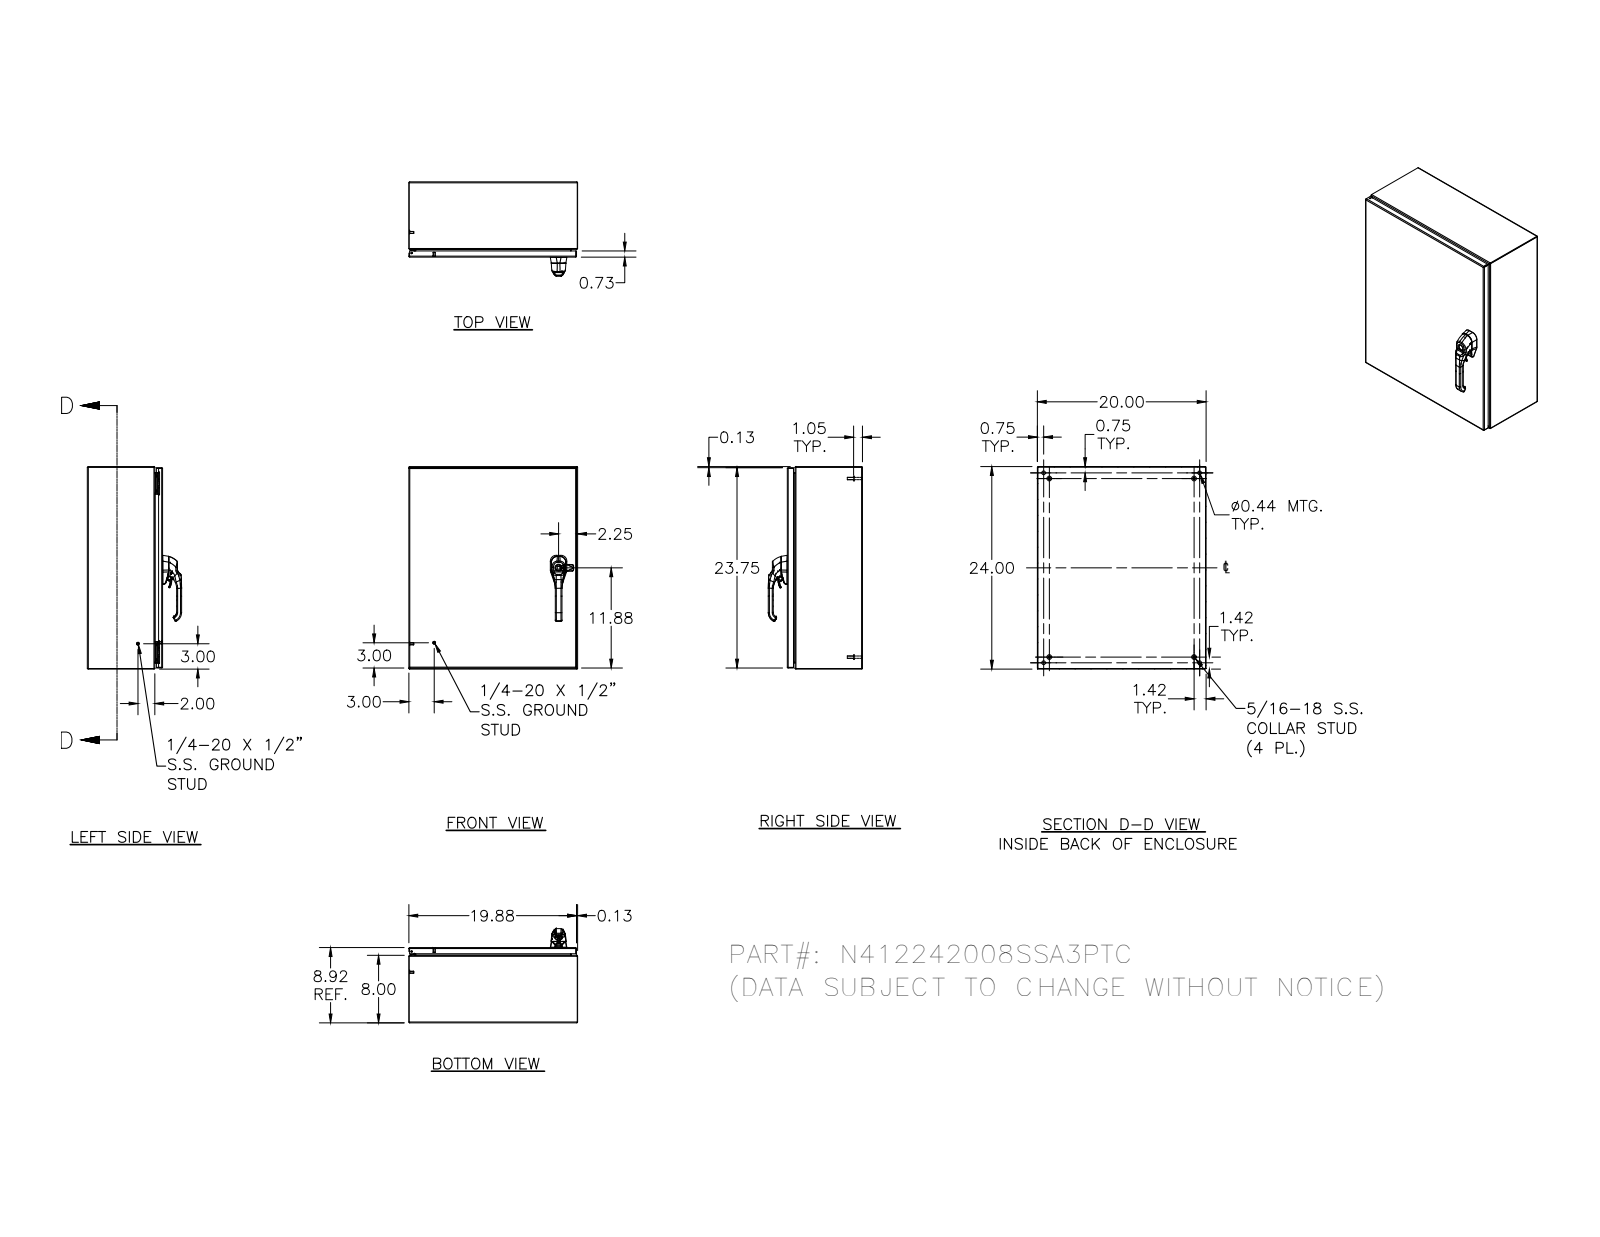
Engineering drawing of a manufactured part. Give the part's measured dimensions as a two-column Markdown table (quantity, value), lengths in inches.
| quantity | value |
| --- | --- |
| part name | N412242008SSA3PTC; N412242008SSA3PTCBKP; N4122420SSA3PTCLID; HFW328176 (+8 more) |
| STEP written by | Autodesk Inventor 2011 (AUTOMOTIVE_DESIGN) |
| units | inches |
| bodies | 41 solids, 2769 faces (882 planar, 1022 cylindrical, 865 other) |
| overall size | 24 × 20 × 11.166 |
| volume | 143.2 in³ |
| surface area | 3 791 in² |
| round holes (diameter × count) | 0.188 × 5, 0.093 × 4, 0.152 × 4, 0.167 × 4, 0.172 × 4, 0.437 × 4, 0.213 × 3, 0.156 × 2, 0.315 × 2, 0.402 × 2, 0.413 × 2, 0.122 × 1 |
| round bosses / shafts (diameter × count) | 0.25 × 10, 0.563 × 4, 0.36 × 4, 0.32 × 4, 0.3 × 4, 0.275 × 4, 0.256 × 4, 0.164 × 4 |
| partial cylindrical surfaces (radius × count) | 0.02 × 173, 0.012 × 100, 0.031 × 30, 0.05 × 26, 0.019 × 21, 0.105 × 20, 0.016 × 18, 0.079 × 14 |
| main face-to-face distances | 0.074, 8.843, 8.917, 8.769, 19.926, 23.926, 19.852, 20, 24, 23.852 |
| hole center spacings | 19.996, 18.872, 0.017, 0.66, 20.656, 0.019, 0.5, 0.648 |
